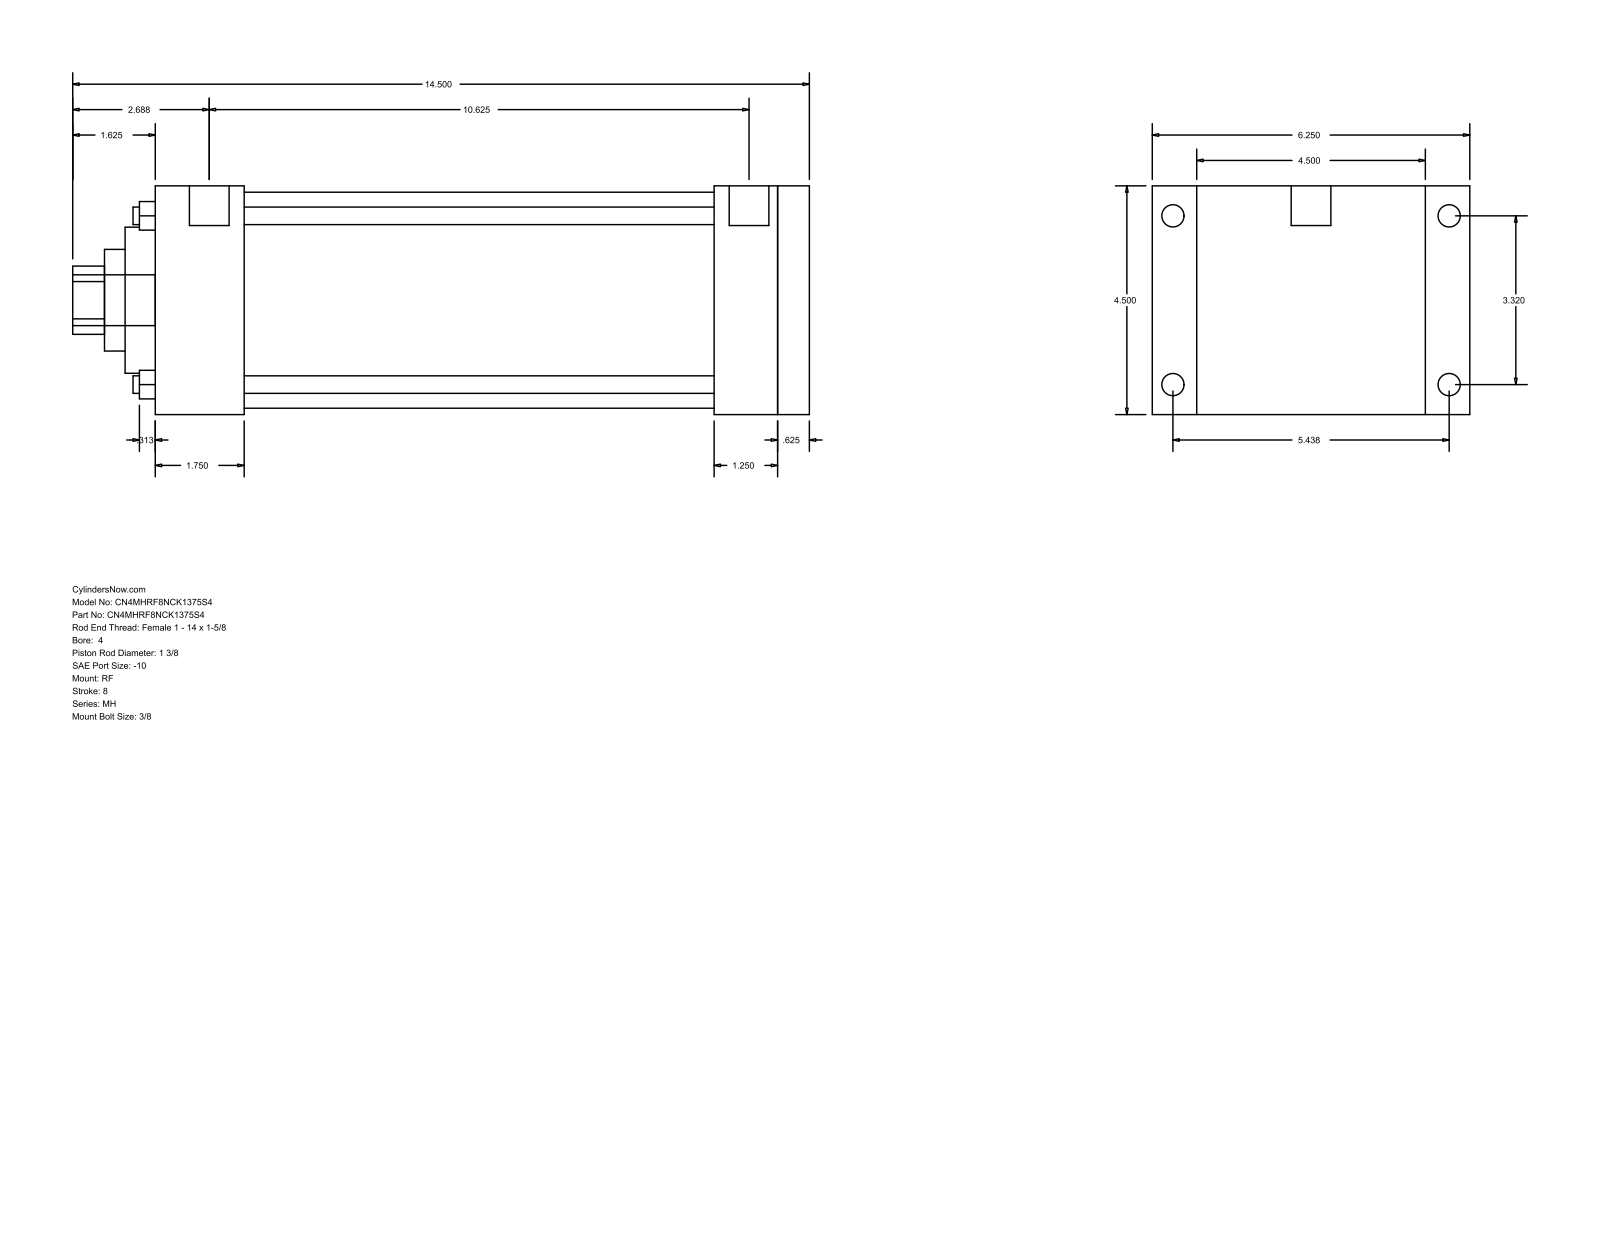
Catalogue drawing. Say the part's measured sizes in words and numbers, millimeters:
The part is named "MH_RF__0400_1.375". Its 3-D file was written by "GSSL Pune (CONFIG_CONTROL_DESIGN)". It is 0 solids with 94 faces: 65 planar, 29 cylindrical and 0 other. Overall it measures 368.3 by 158.75 by 114.3 millimeters. Round holes: 4 of diameter 8.76, 1 of diameter 34.92, 1 of diameter 50.8, 1 of diameter 73.03, 1 of diameter 107.95. Round bosses or shafts: 4 of diameter 11.13, 4 of diameter 8.73, 2 of diameter 19.84, 1 of diameter 25.4. Partial cylindrical surfaces (rounded edges, fillets, slot ends): 1 of radius 17.06. The main face-to-face distances are 114.3, 327.03, 311.16, 15.87, 44.45, 266.71, 282.58, 279.41, 234.96, 31.75. The hole center spacings are 59.62, 84.32, 119.25.
